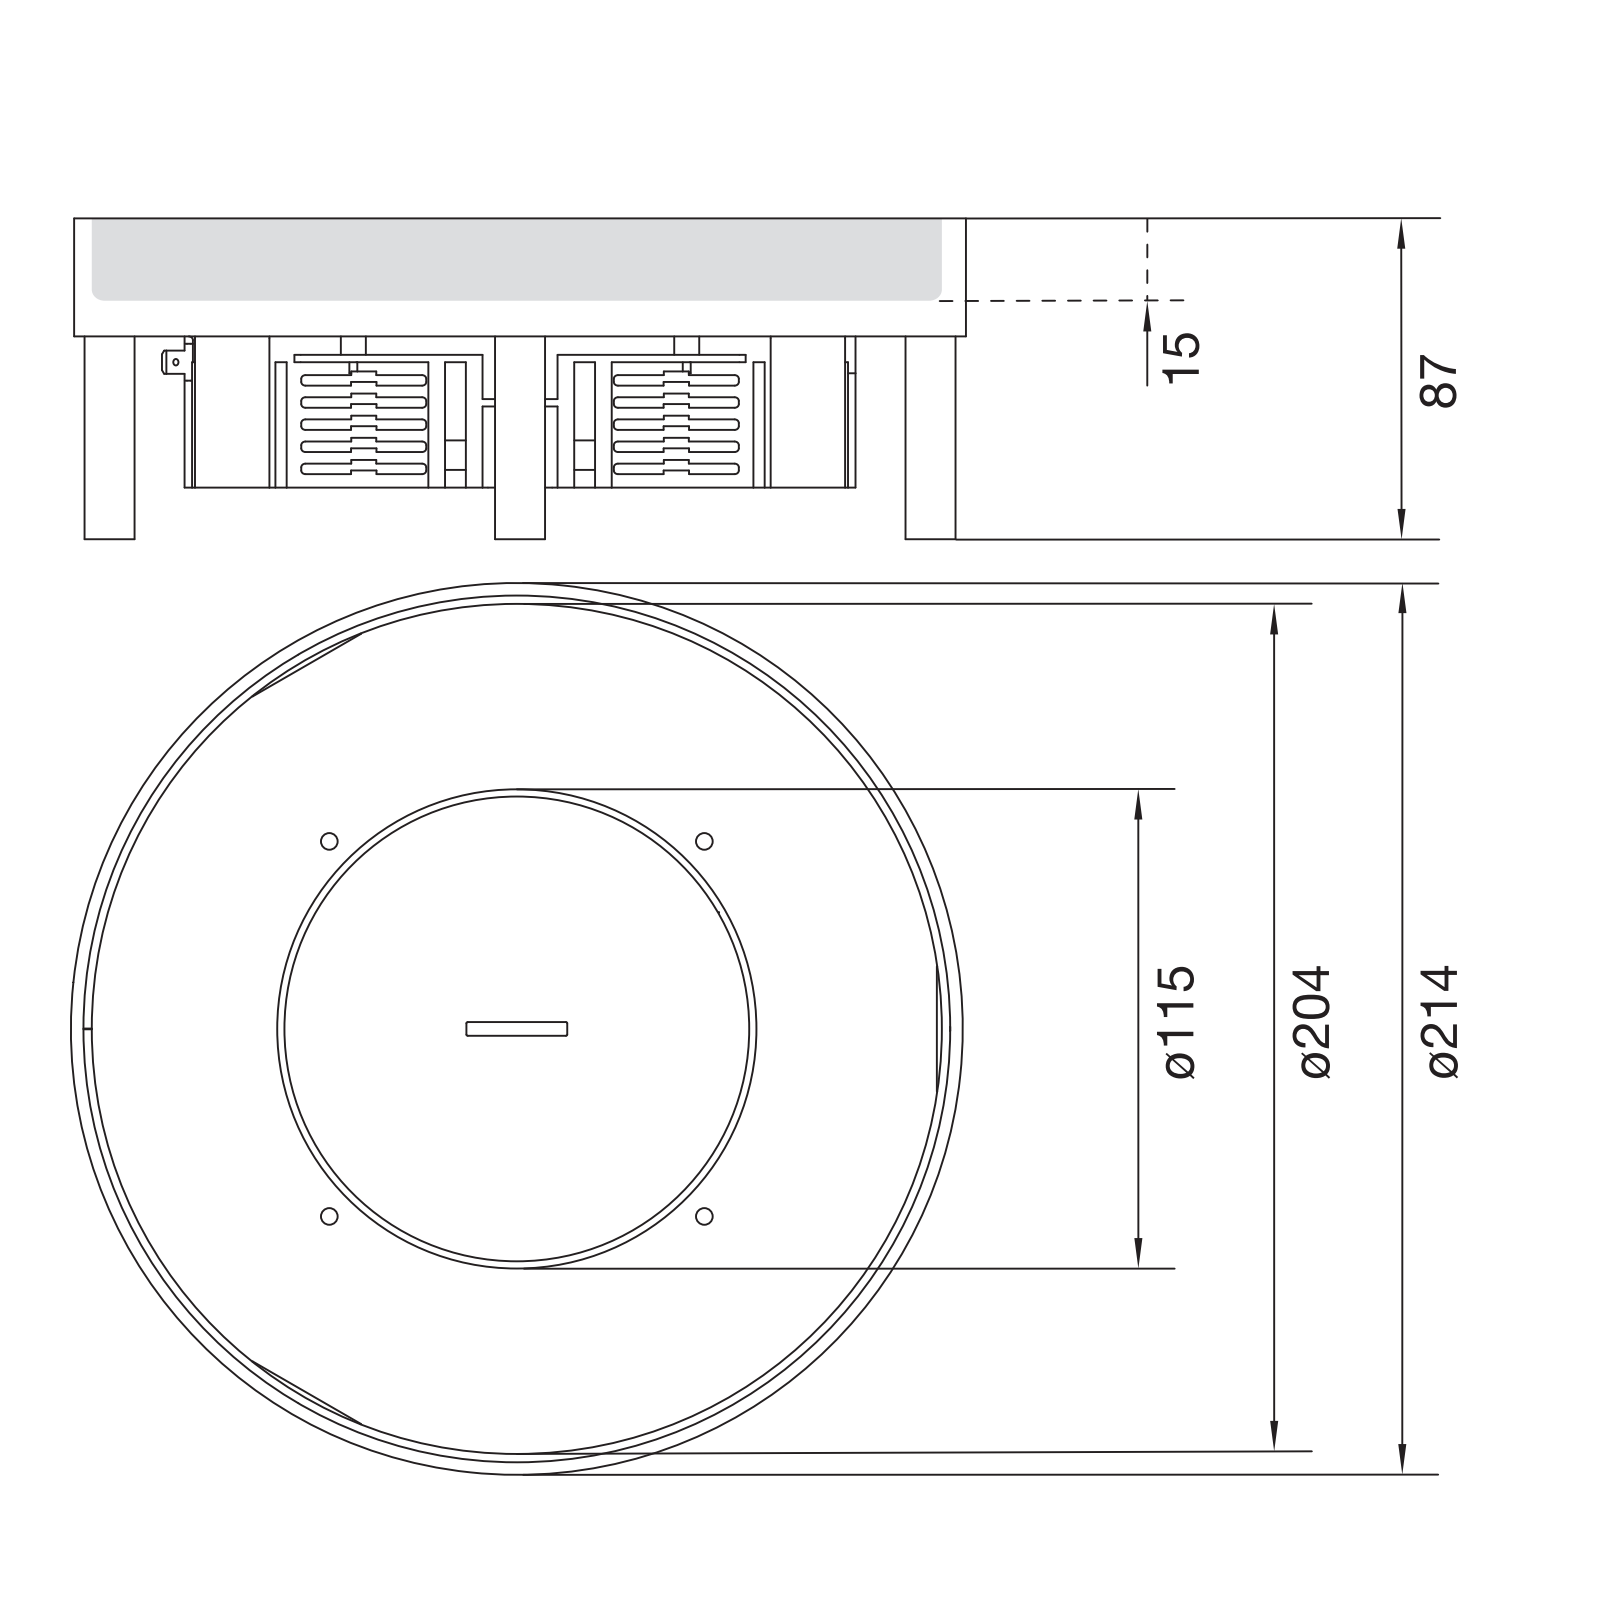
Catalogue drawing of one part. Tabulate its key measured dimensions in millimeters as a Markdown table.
| quantity | value |
| --- | --- |
| part name | T-00671; T-00672; T-00673; T-00675 (+8 more) |
| STEP written by | CREO PARAMETRIC BY PTC INC, 2022024 (AUTOMOTIVE_DESIGN) |
| units | millimeters |
| bodies | 16 solids, 242 faces (111 planar, 121 cylindrical, 10 other) |
| overall size | 214 × 214 × 87 |
| volume | 504 603 mm³ |
| surface area | 324 864 mm² |
| round holes (diameter × count) | 3.8 × 6, 5 × 4, 6.8 × 4, 8.5 × 4, 10.1 × 4, 4.5 × 3, 80.59 × 1, 90 × 1, 101 × 1, 107 × 1, 108.6 × 1, 112 × 1 |
| round bosses / shafts (diameter × count) | 12 × 4, 9.85 × 4, 214 × 1, 208 × 1, 207 × 1, 204 × 1, 115 × 1, 111 × 1 |
| partial cylindrical surfaces (radius × count) | 0.5 × 8, 5 × 3, 43 × 1 |
| main face-to-face distances | 15, 2, 17, 12, 10, 2.5, 27, 153.5, 5, 32 |
| hole center spacings | 69.91, 150.39, 41.16, 44.08, 63.64, 90, 95.62, 97.39 |
